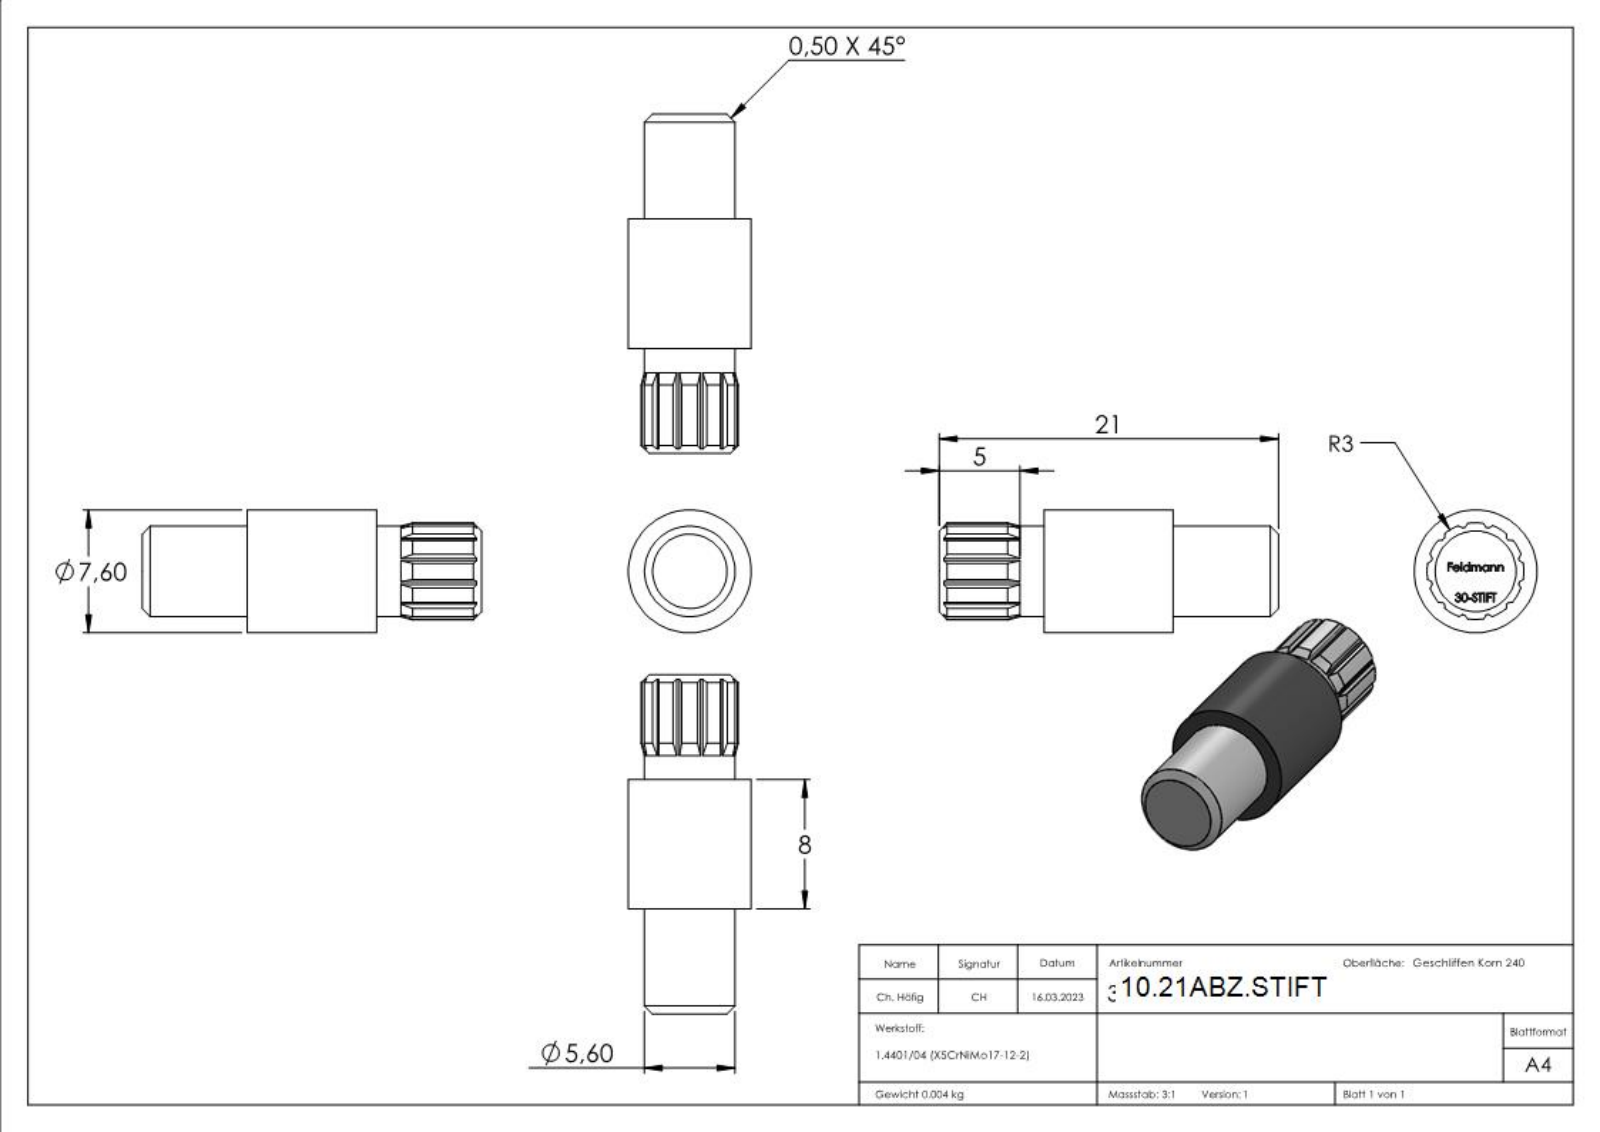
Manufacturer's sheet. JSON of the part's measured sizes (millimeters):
{"part_name": "30-STIFT; 30-STIFT Teil2_30-STIFT Teil2 Keyshot; 30-STIFT Teil1_30-STIFT Teil1 Keyshot", "step_written_by": "SolidWorks 2018 (CONFIG_CONTROL_DESIGN)", "units": "millimeters", "bodies": {"solids": 2, "faces": 208, "planar": 28, "cylindrical": 63, "other": 117}, "overall_size": [21, 7.6, 7.6], "volume_mm3": 692, "surface_area_mm2": 793, "round_holes": [[5.6, 1]], "round_bosses_or_shafts": [[7.6, 1]], "partial_cylinders_radius": [[0.1, 48], [3, 1]], "face_to_face_distances": [6.5, 14.5, 8, 21, 4.04, 4.02]}
